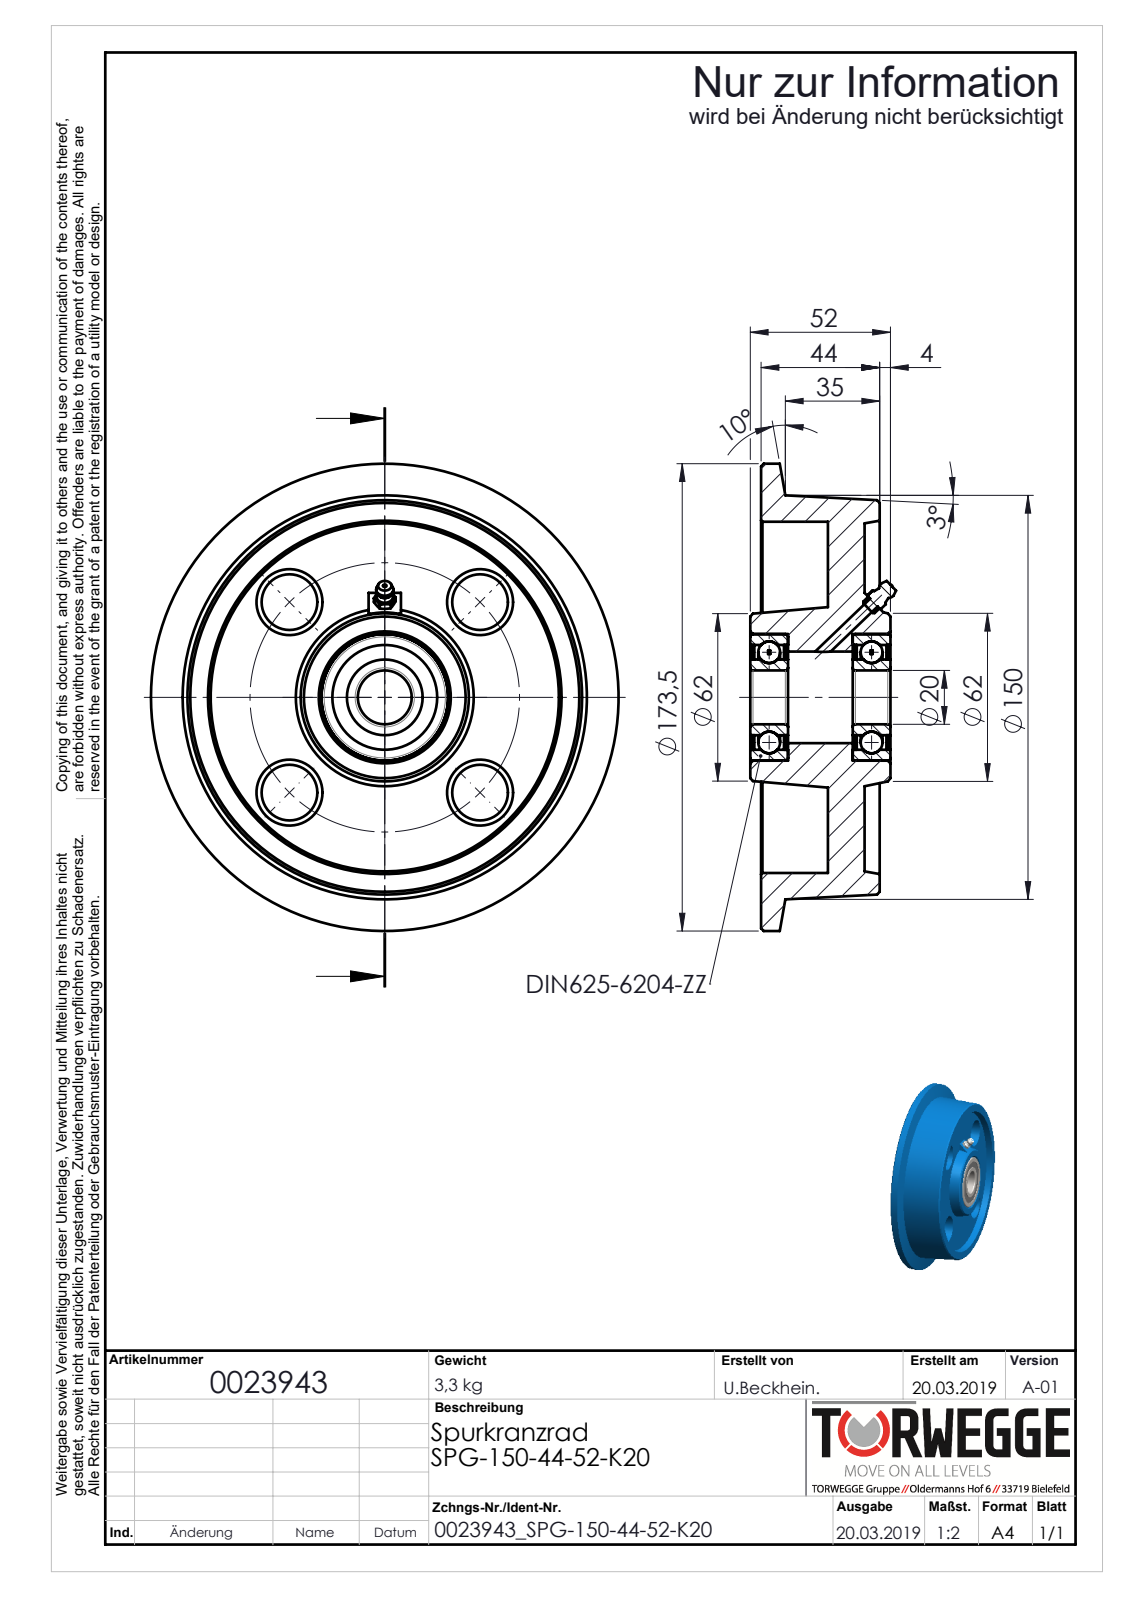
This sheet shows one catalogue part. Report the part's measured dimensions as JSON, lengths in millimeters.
{"part_name": "0023943_SPG-150-44-52-K20_(A-01)", "step_written_by": "SolidWorks 2018 (AUTOMOTIVE_DESIGN)", "units": "millimeters", "bodies": {"solids": 14, "faces": 186, "planar": 46, "cylindrical": 58, "other": 82}, "overall_size": [173.5, 173.5, 54.09], "volume_mm3": 470899, "surface_area_mm2": 116623, "round_holes": [[4, 1], [20, 1], [28.1, 1], [34, 1], [38.9, 1], [47, 1], [130.4, 1]], "round_bosses_or_shafts": [[173.5, 1], [6, 1]], "partial_cylinders_radius": [[16.07, 1], [17.43, 1]], "face_to_face_distances": [24.8, 38.4, 13.6, 38, 4, 48, 14, 10, 34, 44]}
